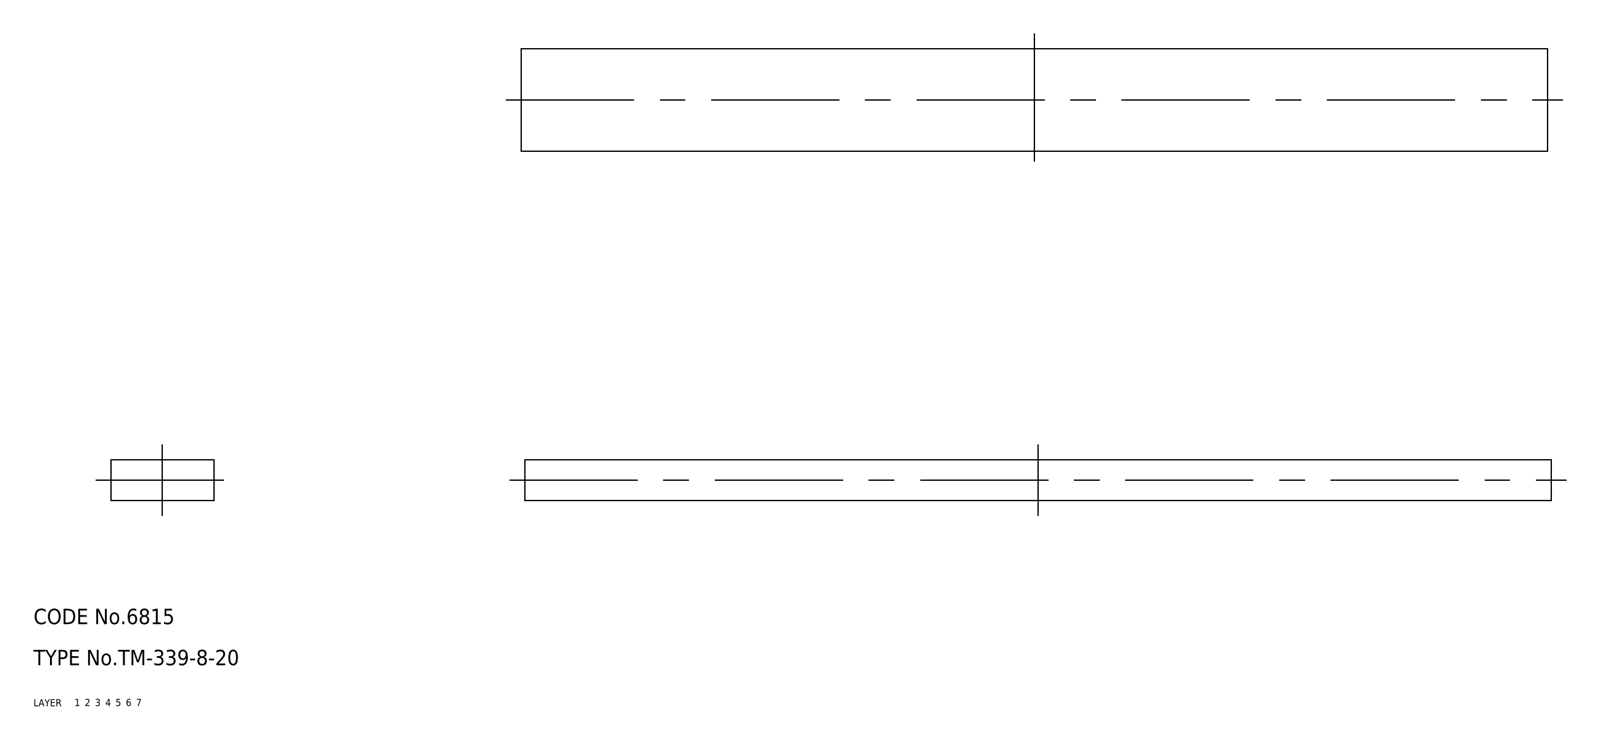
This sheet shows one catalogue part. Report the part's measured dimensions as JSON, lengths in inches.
{"part_name": "rubber foam", "step_written_by": "CADfix (AUTOMOTIVE_DESIGN)", "units": "inches", "bodies": {"solids": 1, "faces": 6, "planar": 0, "cylindrical": 0, "other": 6}, "overall_size": [7.874, 0.787, 0.315], "volume_in3": 1.953, "surface_area_in2": 17.86}
